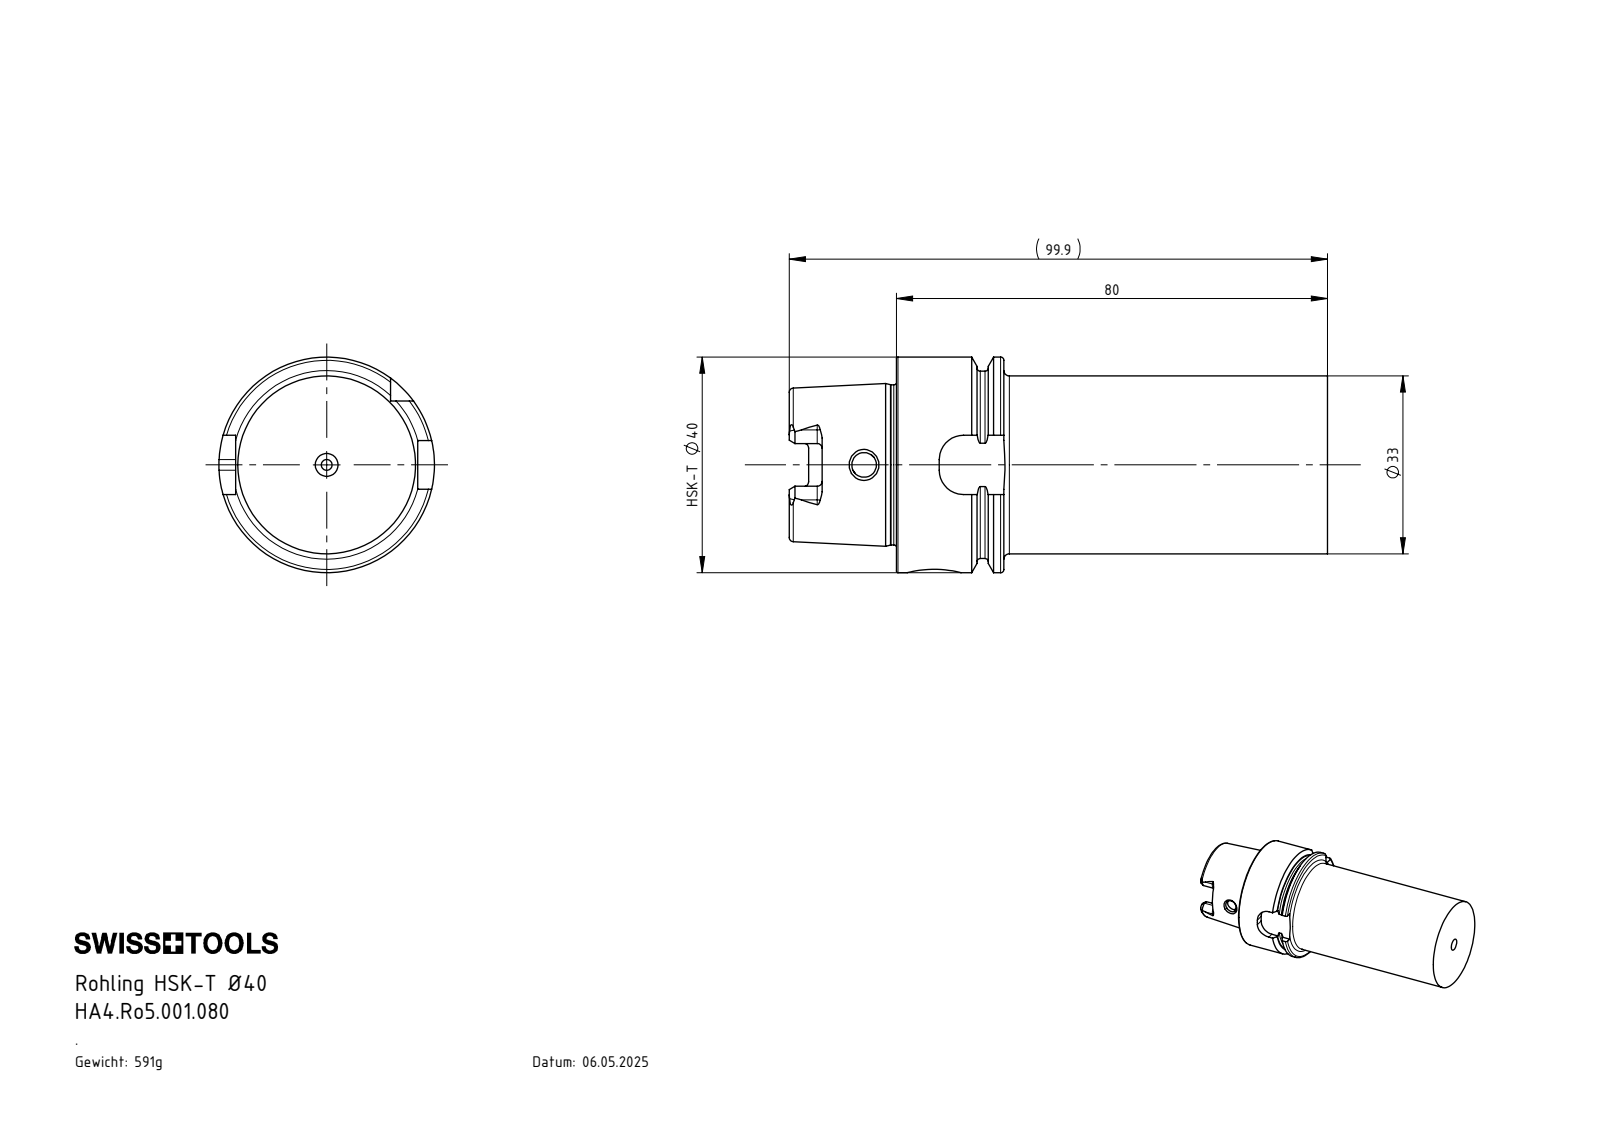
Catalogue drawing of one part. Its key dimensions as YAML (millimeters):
part_name: "HA4.Ro5.001.080"
step_written_by: "SolidWorks 2022 (AUTOMOTIVE_DESIGN)"
units: millimeters
bodies: {solids: 1, faces: 161, planar: 46, cylindrical: 48, other: 67}
overall_size: [99.9, 40, 40]
volume: 75315
surface_area: 15882
round_holes:
  - {diameter: 2, count: 1}
  - {diameter: 4.6, count: 1}
  - {diameter: 5, count: 1}
  - {diameter: 10, count: 1}
  - {diameter: 11, count: 1}
  - {diameter: 12.5, count: 1}
  - {diameter: 21, count: 1}
  - {diameter: 25.5, count: 1}
round_bosses_or_shafts:
  - {diameter: 40, count: 1}
  - {diameter: 34.75, count: 1}
  - {diameter: 33, count: 1}
  - {diameter: 29.71, count: 1}
partial_cylinders:
  - {radius: 0.9, count: 6}
  - {radius: 1.88, count: 4}
  - {radius: 4.5, count: 4}
face_to_face_distances: [80, 7.95, 72.05, 19.95, 12, 60.05, 19.9, 27.85, 39.85, 99.9]
